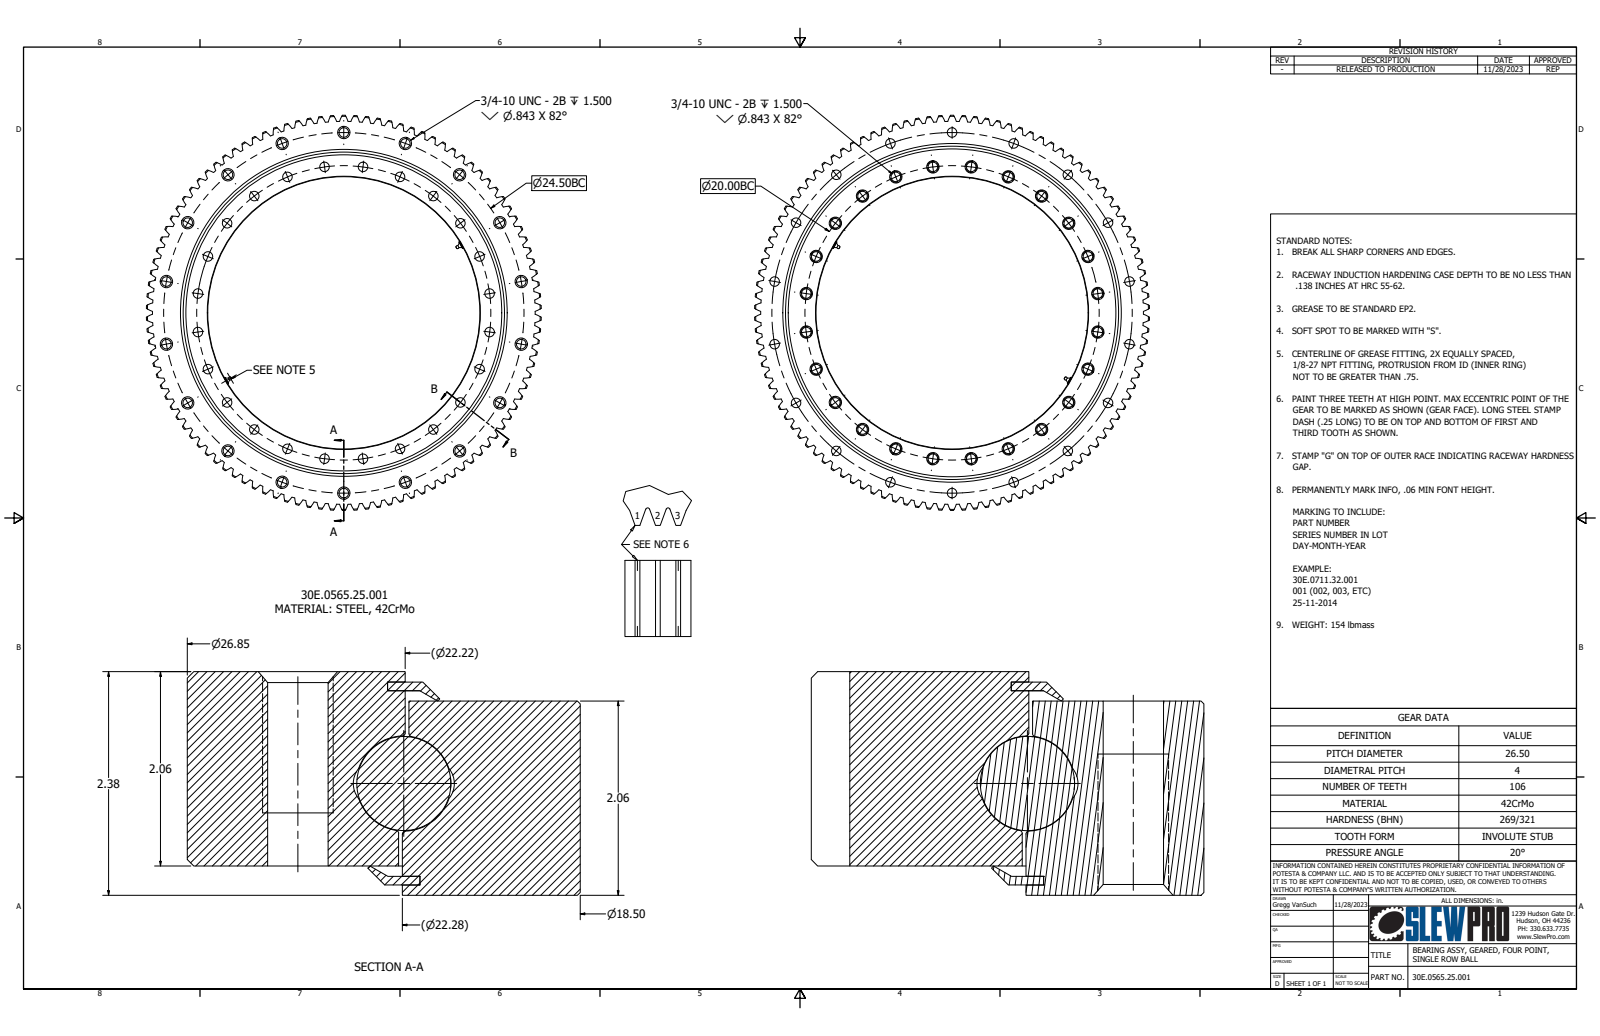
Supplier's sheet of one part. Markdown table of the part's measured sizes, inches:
| quantity | value |
| --- | --- |
| part name | 30E.0565.25.001; Spur Gears1; 1_8 NPT Fitting |
| STEP written by | Autodesk Inventor 2026 (AUTOMOTIVE_DESIGN) |
| units | inches |
| bodies | 8 solids, 932 faces (34 planar, 486 cylindrical, 412 other) |
| overall size | 26.849 × 26.843 × 2.375 |
| volume | 541.3 in³ |
| surface area | 1 914 in² |
| round holes (diameter × count) | 0.642 × 42, 0.1 × 2, 1.095 × 1, 18.5 × 1, 21.907 × 1, 22.22 × 1, 22.36 × 1, 22.595 × 1 |
| round bosses / shafts (diameter × count) | 22.593 × 1, 22.28 × 1, 22.14 × 1, 21.905 × 1, 1.094 × 1 |
| partial cylindrical surfaces (radius × count) | 2.278 × 212, 13.012 × 1, 13.425 × 1 |
| main face-to-face distances | 2.063, 0.312, 1.751, 2.375, 0.11, 0.202, 0.109, 0.203, 0.093, 2.265 |
| hole center spacings | 10, 19.829, 12.175, 14.142, 15.867, 17.32, 18.478, 19.319 |
